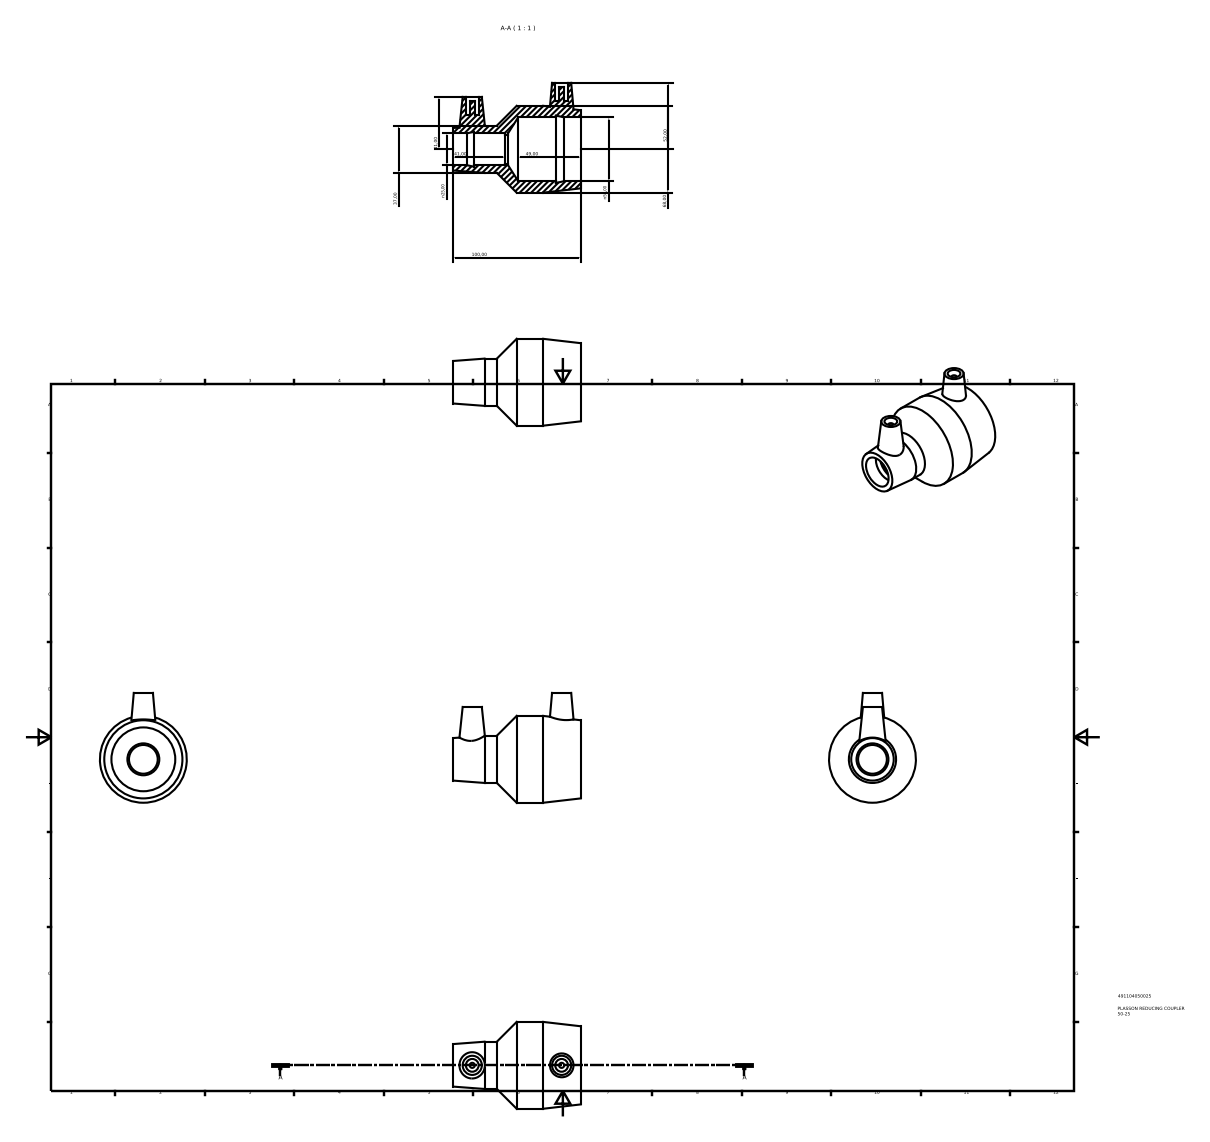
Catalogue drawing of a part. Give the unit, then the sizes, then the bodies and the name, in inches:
Units: inches
Overall size (bounding box): 3.937 × 3.386 × 2.677
Round holes (diameter × count): ⌀0.394 ×2, ⌀0.886 ×1, ⌀0.984 ×1, ⌀1.969 ×1
Round bosses / shafts (diameter × count): ⌀0.157 ×2, ⌀2.677 ×1, ⌀1.457 ×1
Main face-to-face distances: 3.937, 3.165, 0.772, 0.433, 0.551, 0.646, 2.52, 3.291, 1.695, 1.049
Hole centre spacings: 2.756
Volume: 7.444 in³ · Surface area: 55.85 in²
Bodies: 1 solid, 32 faces (12 planar, 11 cylindrical, 9 other)
Part name (STEP PRODUCT): 491104050025
STEP written by: Autodesk Inventor 2015 (AUTOMOTIVE_DESIGN)
